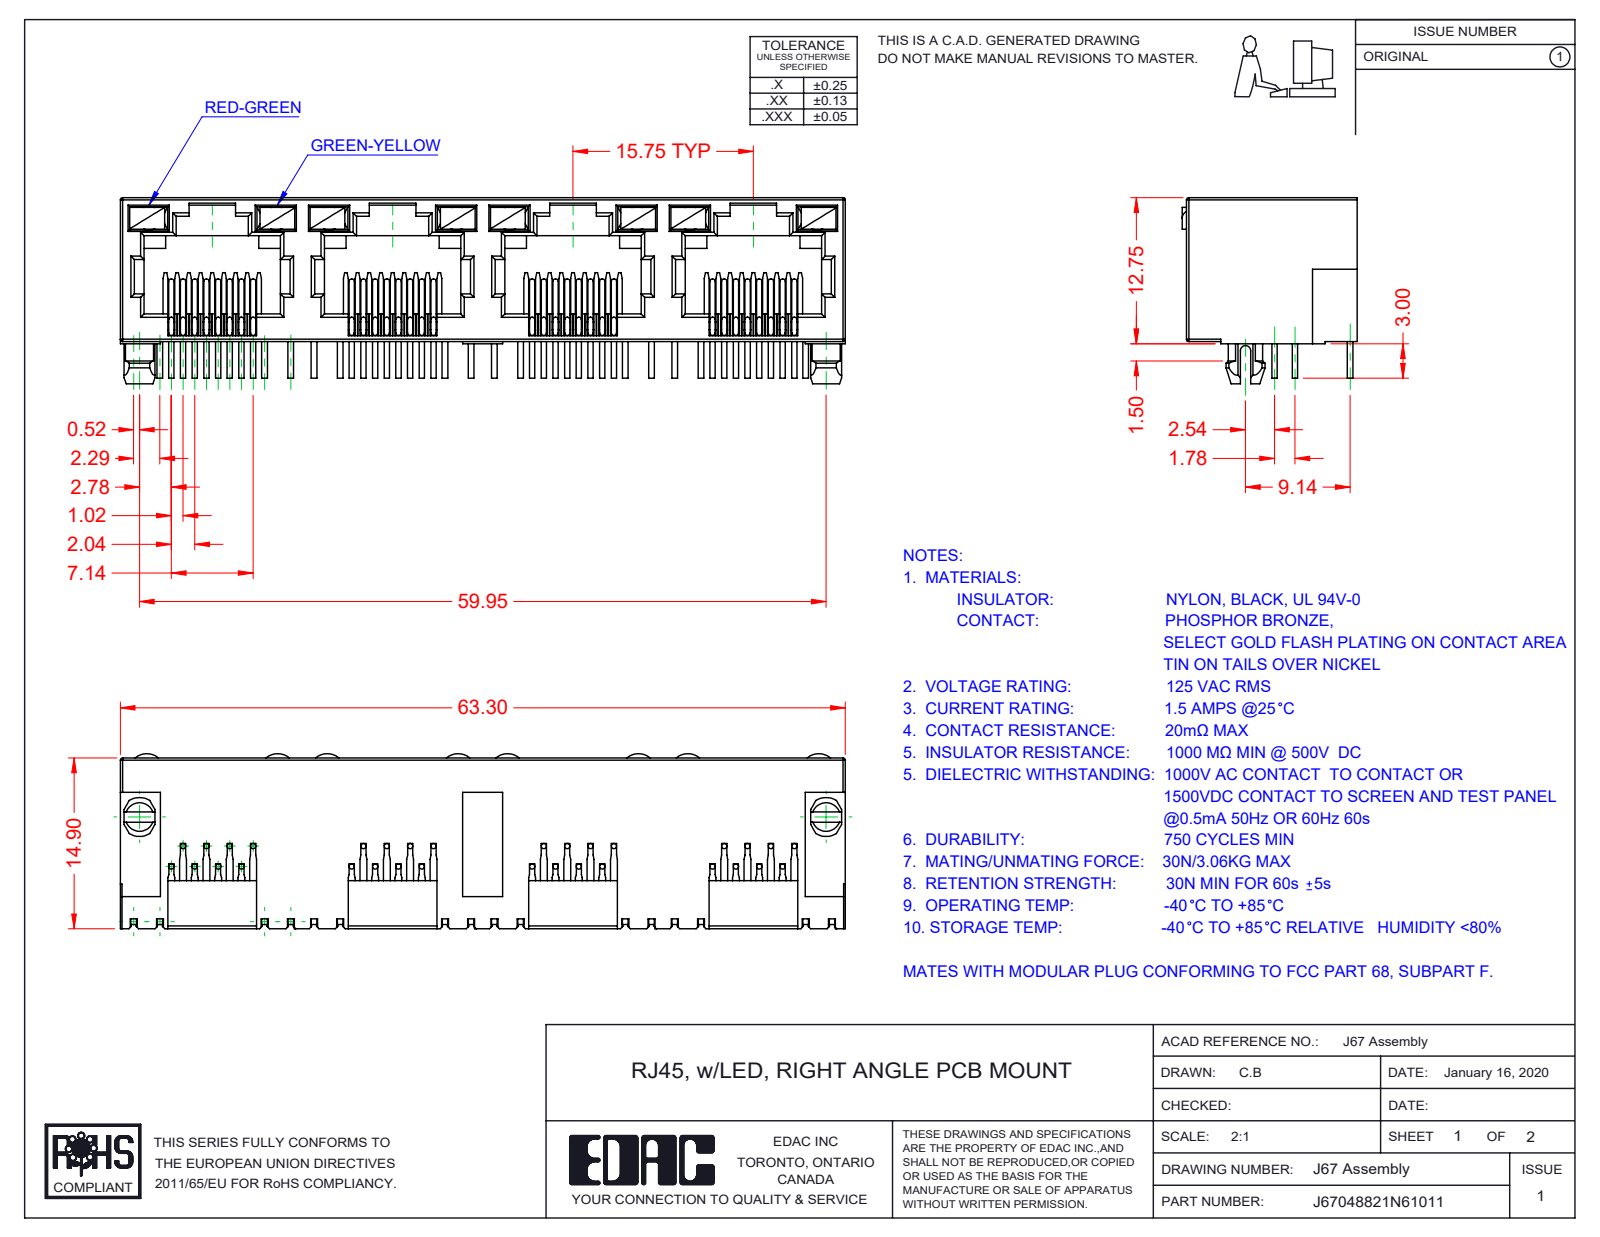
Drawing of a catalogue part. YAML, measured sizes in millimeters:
part_name: "67 Insulator; 67 Contacts; 67 LED LH_6-Red-Green; 67 LED RH_5-Green-Yellow (+1 more)"
step_written_by: "SolidWorks 2016 (CONFIG_CONTROL_DESIGN)"
units: millimeters
bodies: {solids: 41, faces: 2481, planar: 1781, cylindrical: 492, other: 208}
overall_size: [63.3, 16.25, 15.28]
volume: 5159
surface_area: 11573
round_bosses_or_shafts:
  - {diameter: 0.46, count: 96}
partial_cylinders:
  - {radius: 0.2, count: 66}
  - {radius: 0.3, count: 29}
  - {radius: 0.45, count: 9}
  - {radius: 1.55, count: 8}
  - {radius: 1.5, count: 2}
  - {radius: 1.7, count: 2}
  - {radius: 0.35, count: 1}
  - {radius: 1, count: 1}
face_to_face_distances: [0.5, 12.55, 1.89, 0.89, 10, 15.75, 1, 1.39, 11, 11.89]
